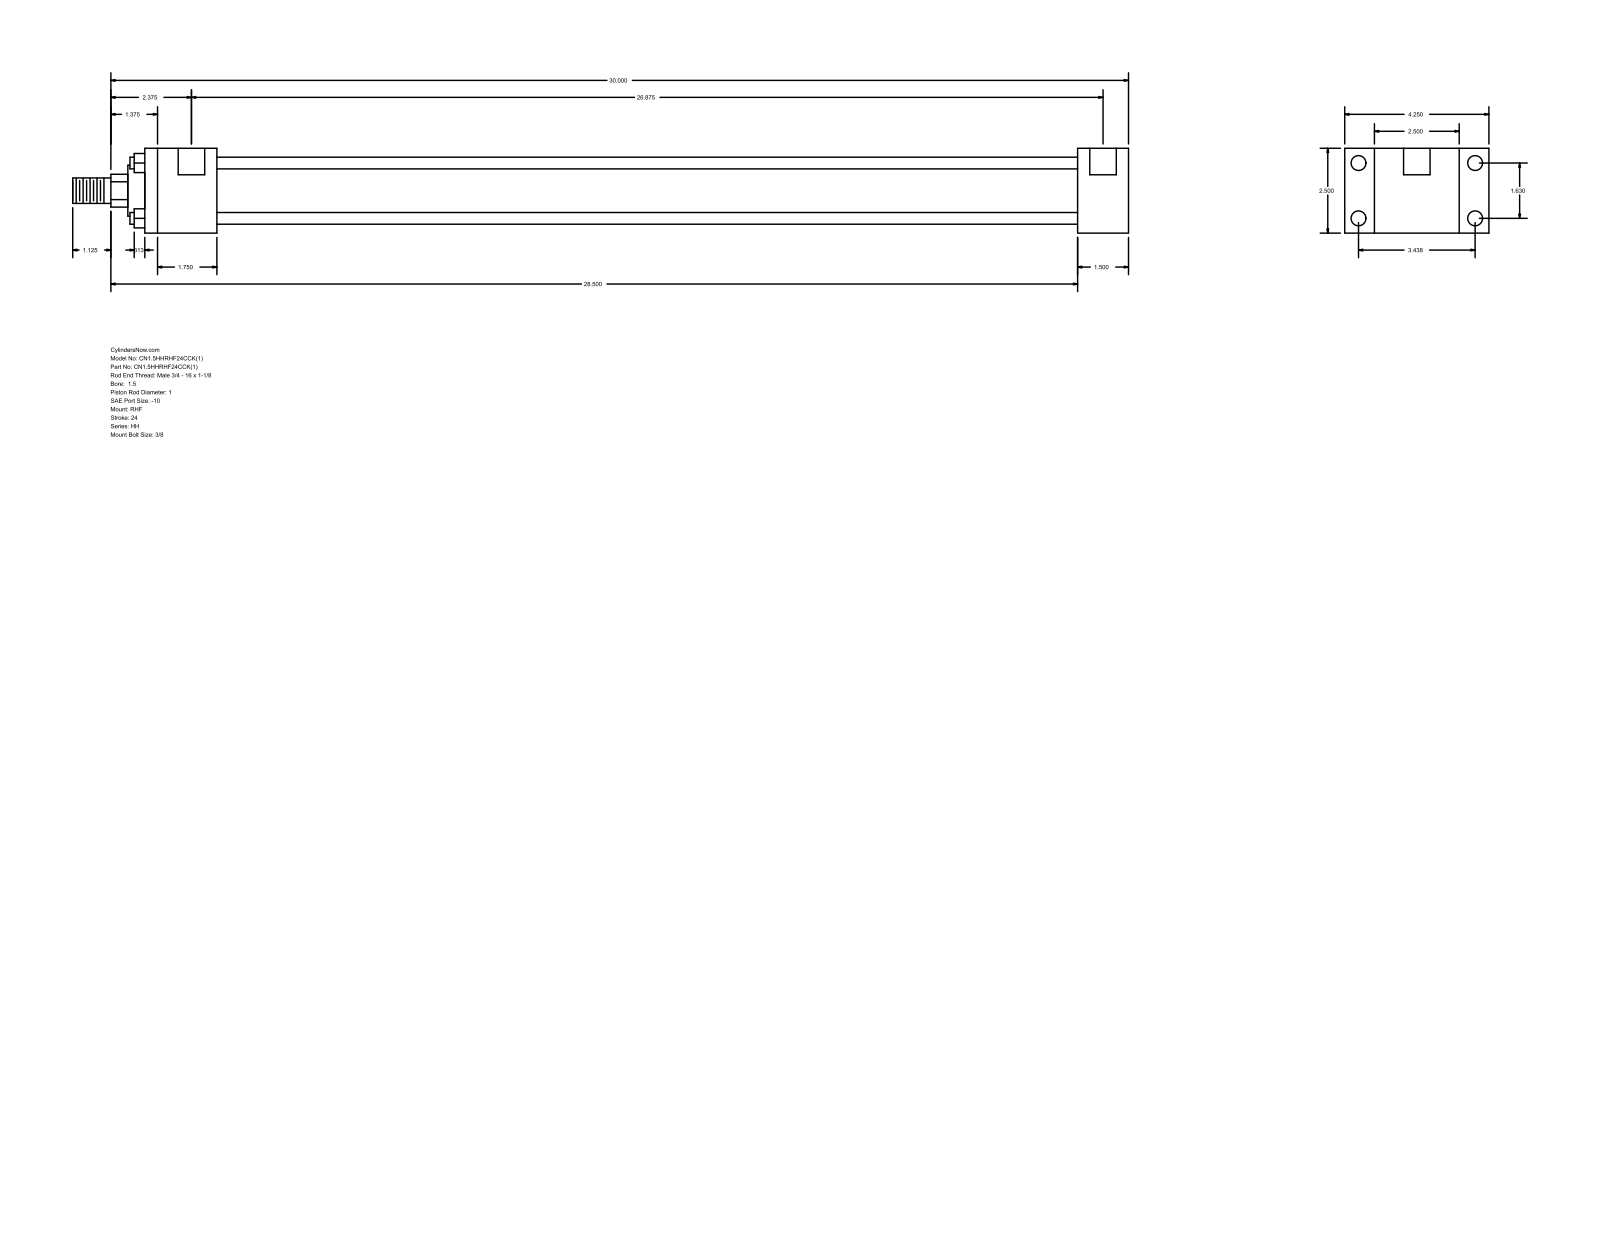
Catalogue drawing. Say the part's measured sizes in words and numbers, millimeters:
The part is named "HH_RHF__0150_1". Its 3-D file was written by "GSSL Pune (CONFIG_CONTROL_DESIGN)". It is 0 solids with 88 faces: 60 planar, 28 cylindrical and 0 other. Overall it measures 790.58 by 107.95 by 63.5 millimeters. Round holes: 4 of diameter 5.56, 4 of diameter 11.13, 2 of diameter 19.84. Round bosses or shafts: 4 of diameter 8.76, 1 of diameter 44.45, 1 of diameter 38.1, 1 of diameter 25.4, 1 of diameter 19.05. Partial cylindrical surfaces (rounded edges, fillets, slot ends): 1 of radius 12.29. The main face-to-face distances are 63.5, 22.23, 85.73, 38.1, 107.96, 644.52, 682.62, 53.98, 698.5, 736.6. The hole center spacings are 1.59, 41.4, 87.32, 96.64, 684.21, 685.8, 682.62.
